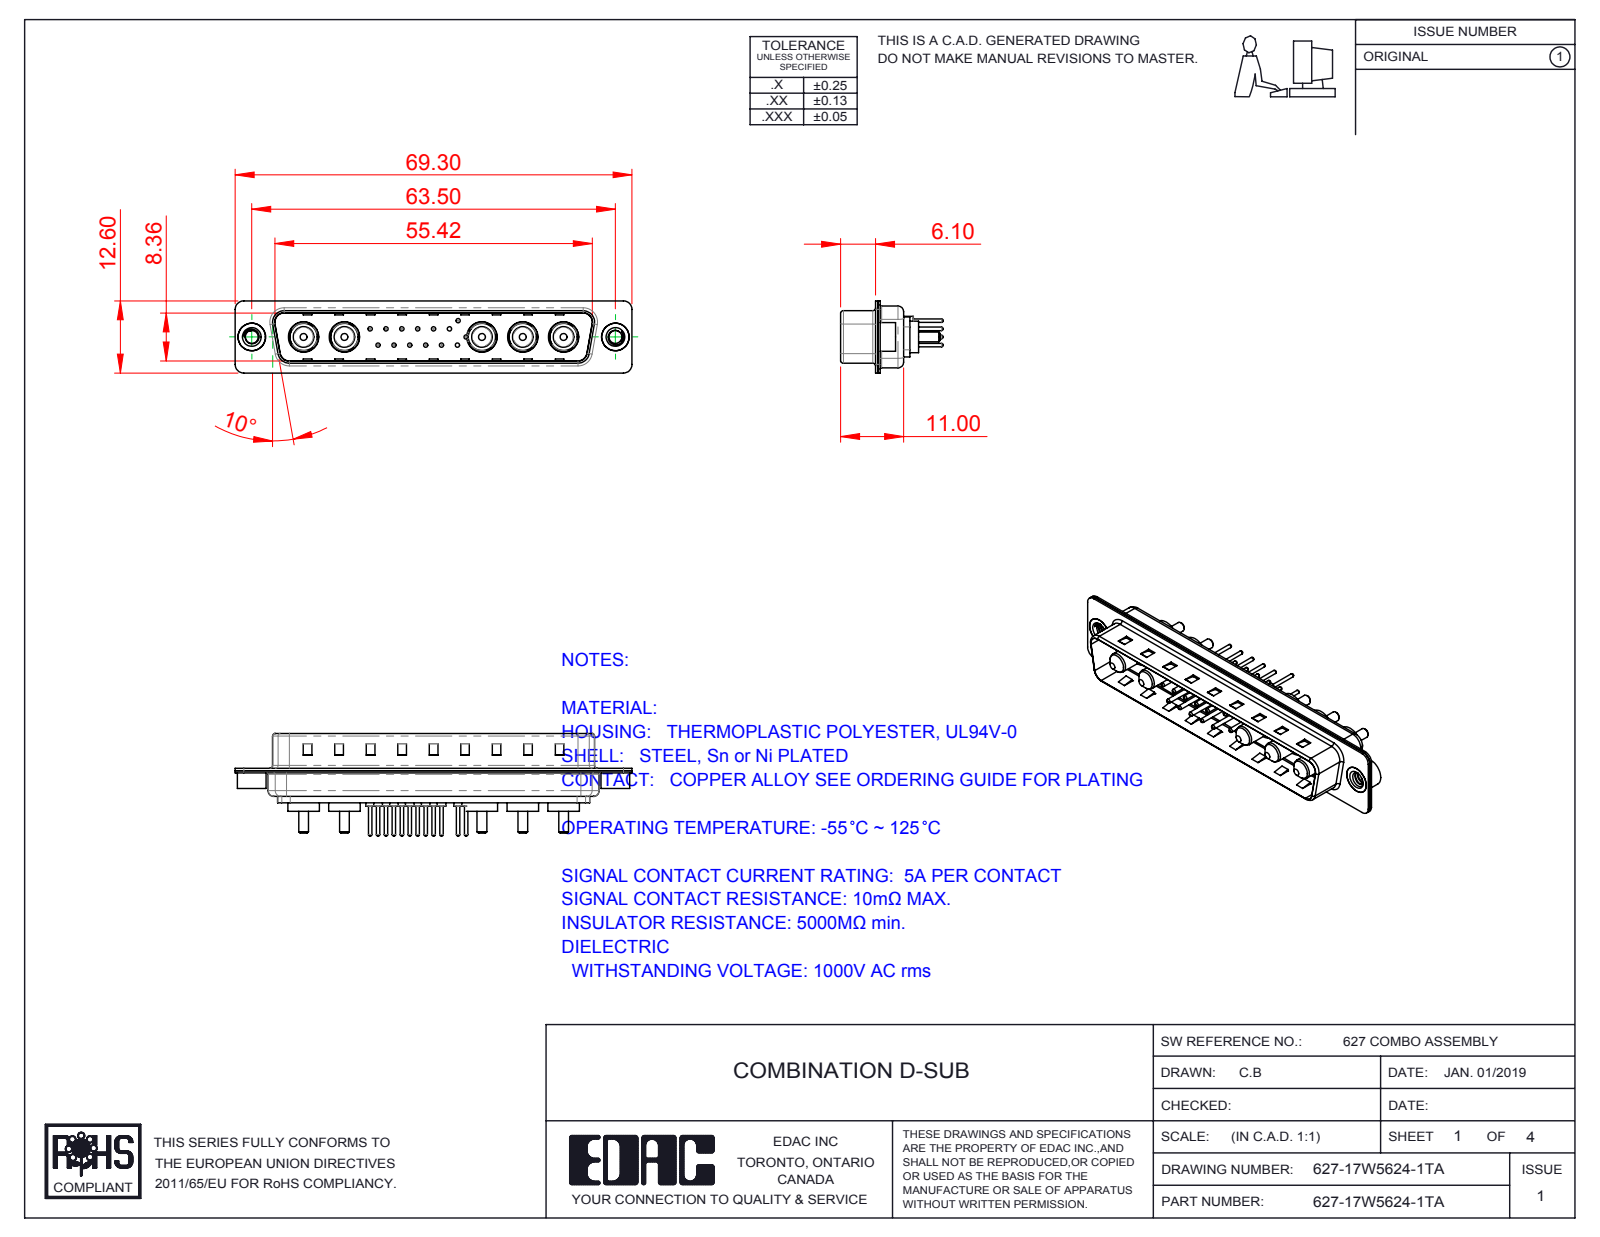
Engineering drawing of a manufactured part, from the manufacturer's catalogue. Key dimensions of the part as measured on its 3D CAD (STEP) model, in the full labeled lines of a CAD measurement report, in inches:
Part name (STEP PRODUCT): 627Combo Housing_17W5; 627Combo Threaded Rivet_A; 627Combo Contact Row 1_24; 627Combo Threaded Rivet_2 (+5 more)
STEP written by: SolidWorks 2016 (CONFIG_CONTROL_DESIGN)
Units: inches
Bodies: 27 solids, 1055 faces (337 planar, 405 cylindrical, 313 other)
Overall size (bounding box): 2.728 × 0.705 × 0.496
Volume: 0.246 in³ · Surface area: 14.01 in²
Round holes (diameter × count): ⌀0.03 ×12, ⌀0.063 ×12, ⌀0.079 ×12, ⌀0.191 ×5, ⌀0.209 ×5, ⌀0.089 ×2, ⌀0.157 ×2, ⌀0.189 ×2
Round bosses / shafts (diameter × count): ⌀0.059 ×12, ⌀0.024 ×12, ⌀0.217 ×5, ⌀0.205 ×5, ⌀0.187 ×5, ⌀0.148 ×5, ⌀0.142 ×5, ⌀0.067 ×5
Partial cylindrical surfaces — rounded edges, fillets, slot ends (radius × count): R0.059 ×16, R0.079 ×12, R0.02 ×8, R0.063 ×8, R0.083 ×5, R0.01 ×4, R0.024 ×4, R0.026 ×4
Main face-to-face distances: 0.016, 0.032, 0.377, 0.345, 0.059, 0.22, 0.048, 0.393, 0.017, 0.361
Hole centre spacings: 0.124, 0.109, 0.218, 0.198, 0.327, 0.198, 0.295, 0.281
